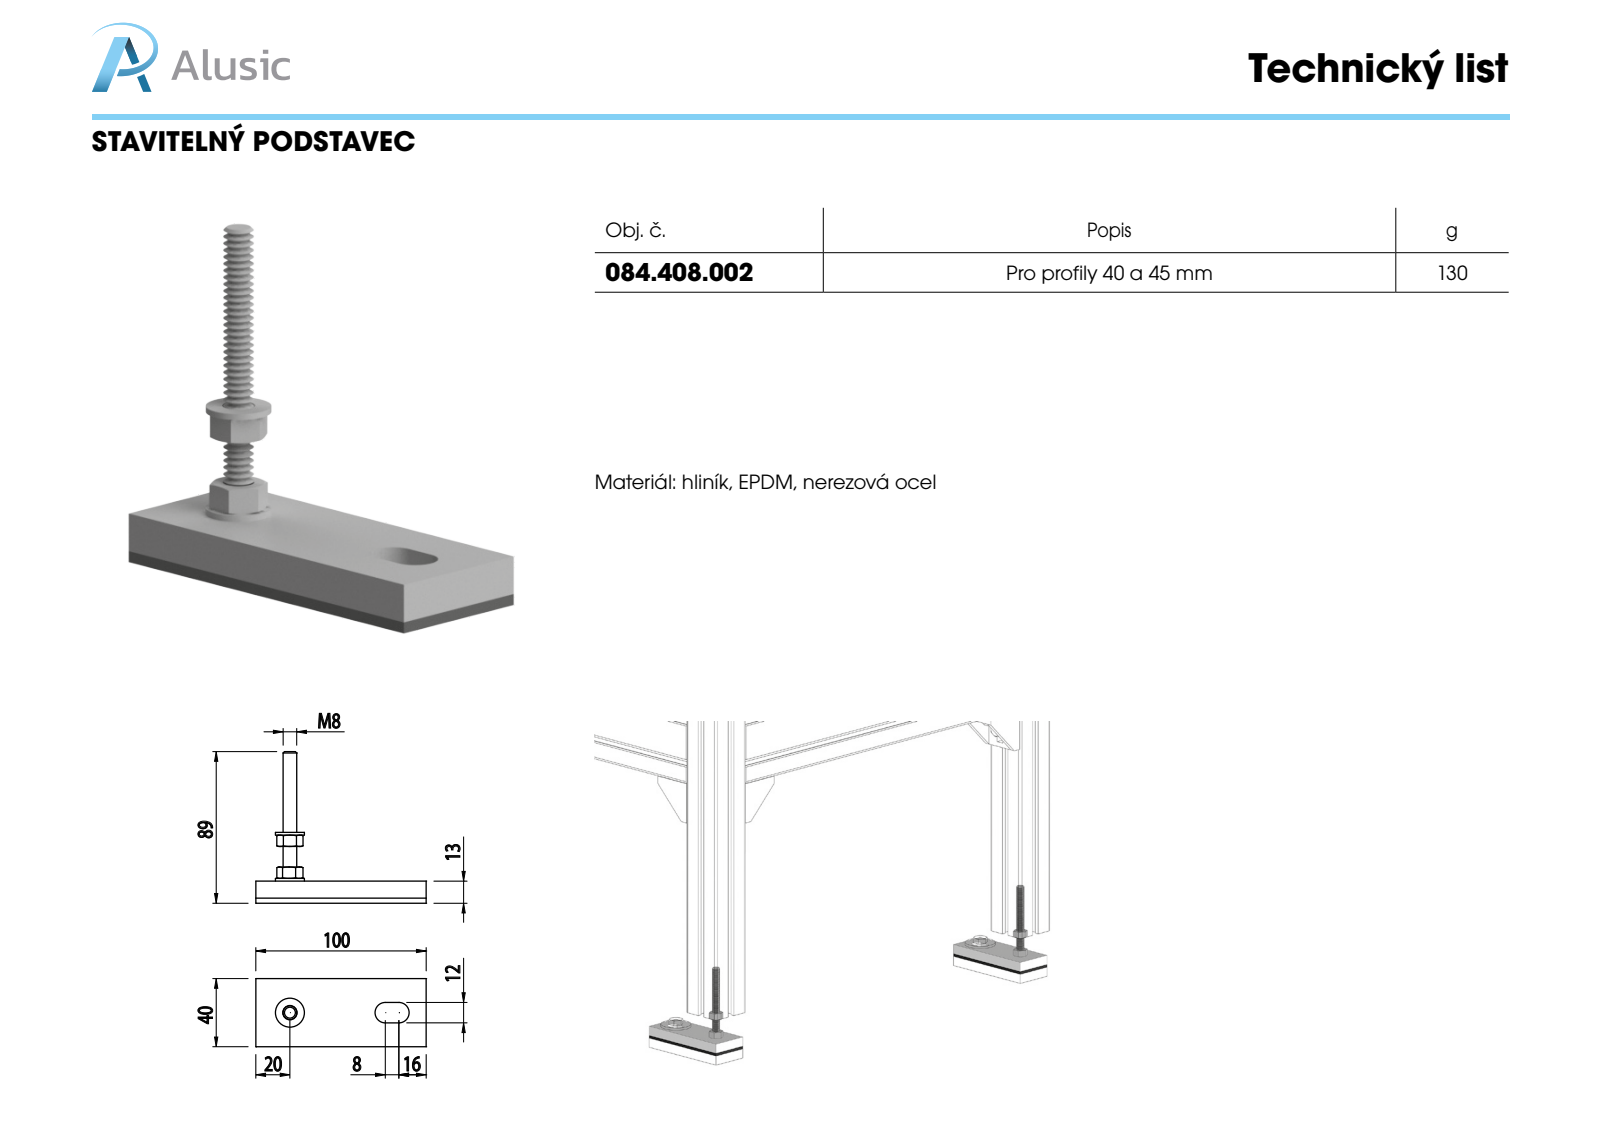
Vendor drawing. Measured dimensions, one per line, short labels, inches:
name: 084.408.002
written by: SolidWorks 2012 (CONFIG_CONTROL_DESIGN)
unit: in
bodies: 7 solids, 100 faces (46 planar, 22 cylindrical, 32 other)
size: 3.937 × 3.504 × 1.575
volume: 3.352 in³; area: 38.09 in²
holes: 1× ⌀0.315, 1× ⌀0.331, 1× ⌀0.354, 1× ⌀0.531
bosses: 1× ⌀0.669
rounds: 2× R0.236
face distances: 0.394, 0.118, 0.512, 1.575, 3.937, 1.063, 0.063, 0.525, 1.457, 0.575
